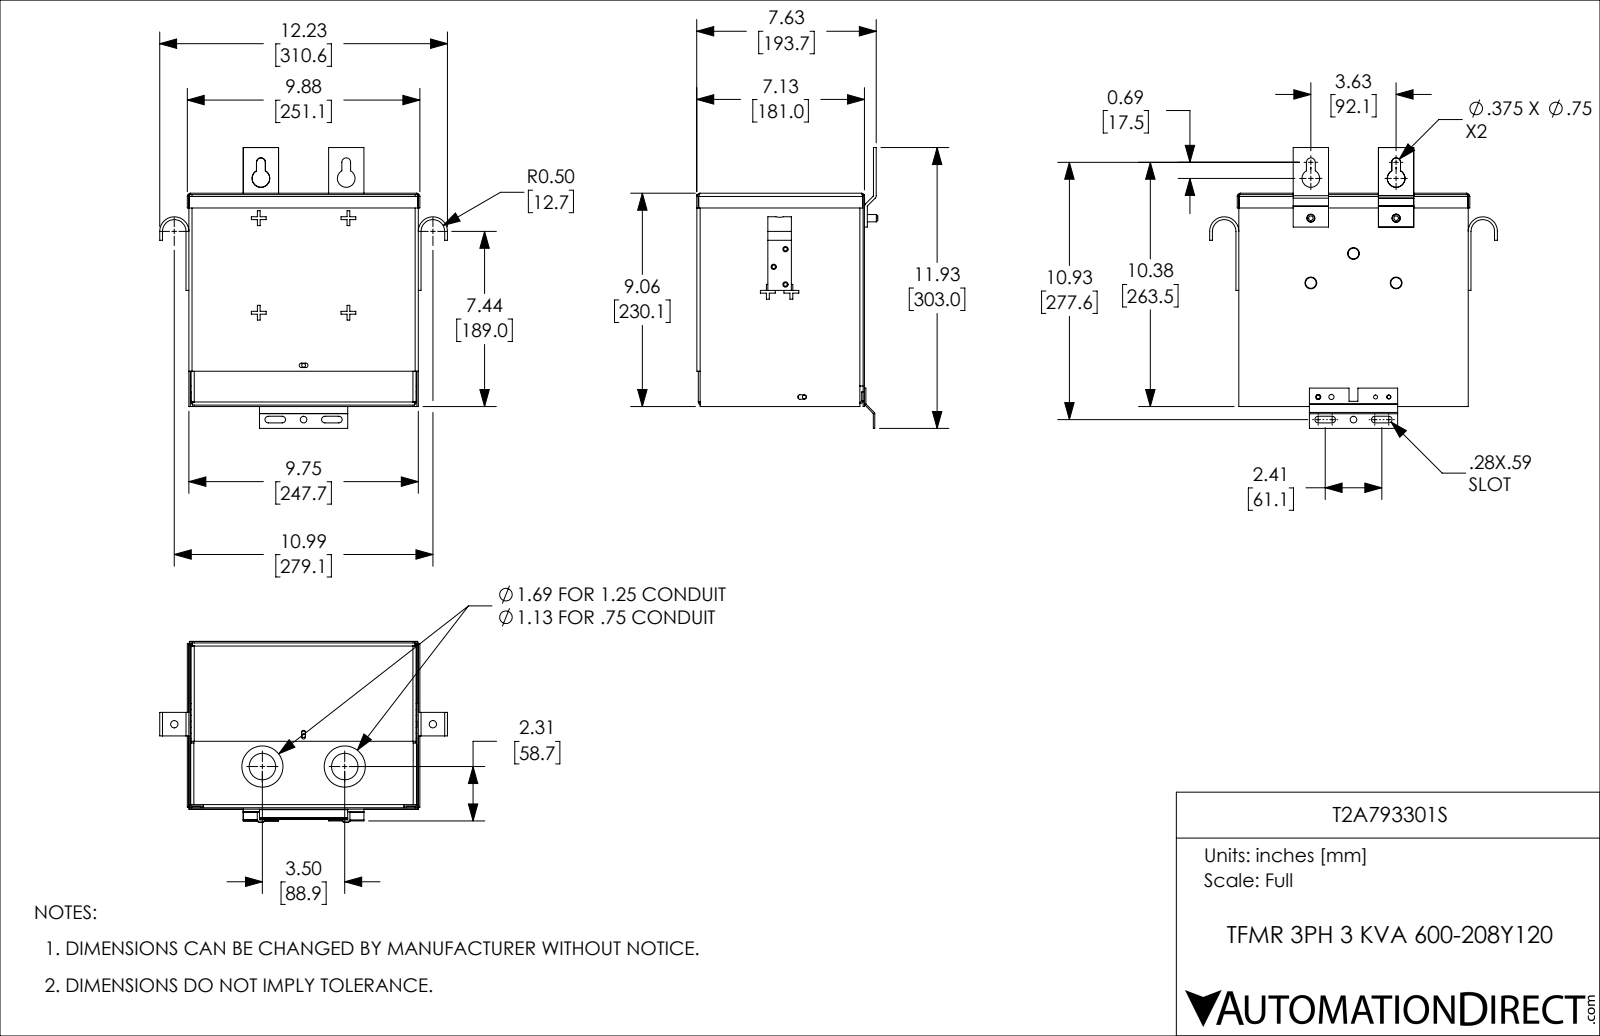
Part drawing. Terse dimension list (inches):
name: T2A793301S
written by: SolidWorks 2017 (AUTOMOTIVE_DESIGN)
unit: in
bodies: 9 solids, 621 faces (405 planar, 144 cylindrical, 72 other)
size: 12.23 × 11.929 × 7.693
volume: 31.98 in³; area: 1 026 in²
holes: 5× ⌀0.16, 2× ⌀0.172, 2× ⌀0.219, 2× ⌀0.281, 2× ⌀0.313, 2× ⌀0.344, 2× ⌀0.75, 2× ⌀1.125, 2× ⌀1.75, 1× ⌀0.173, 1× ⌀0.187
bosses: 2× ⌀1.87, 2× ⌀1.245, 2× ⌀0.312
rounds: 16× R0.075, 16× R0.135, 8× R0.094, 4× R0.141, 2× R0.02, 2× R0.03, 2× R0.078, 2× R0.08
face distances: 0.06, 7.062, 0.059, 7.002, 8.94, 7.122, 9.69, 9.691, 9.75, 9.631
hole spacings: 0.563, 1.342, 1.638, 1.687, 1.781, 2.014, 2.187, 2.437
